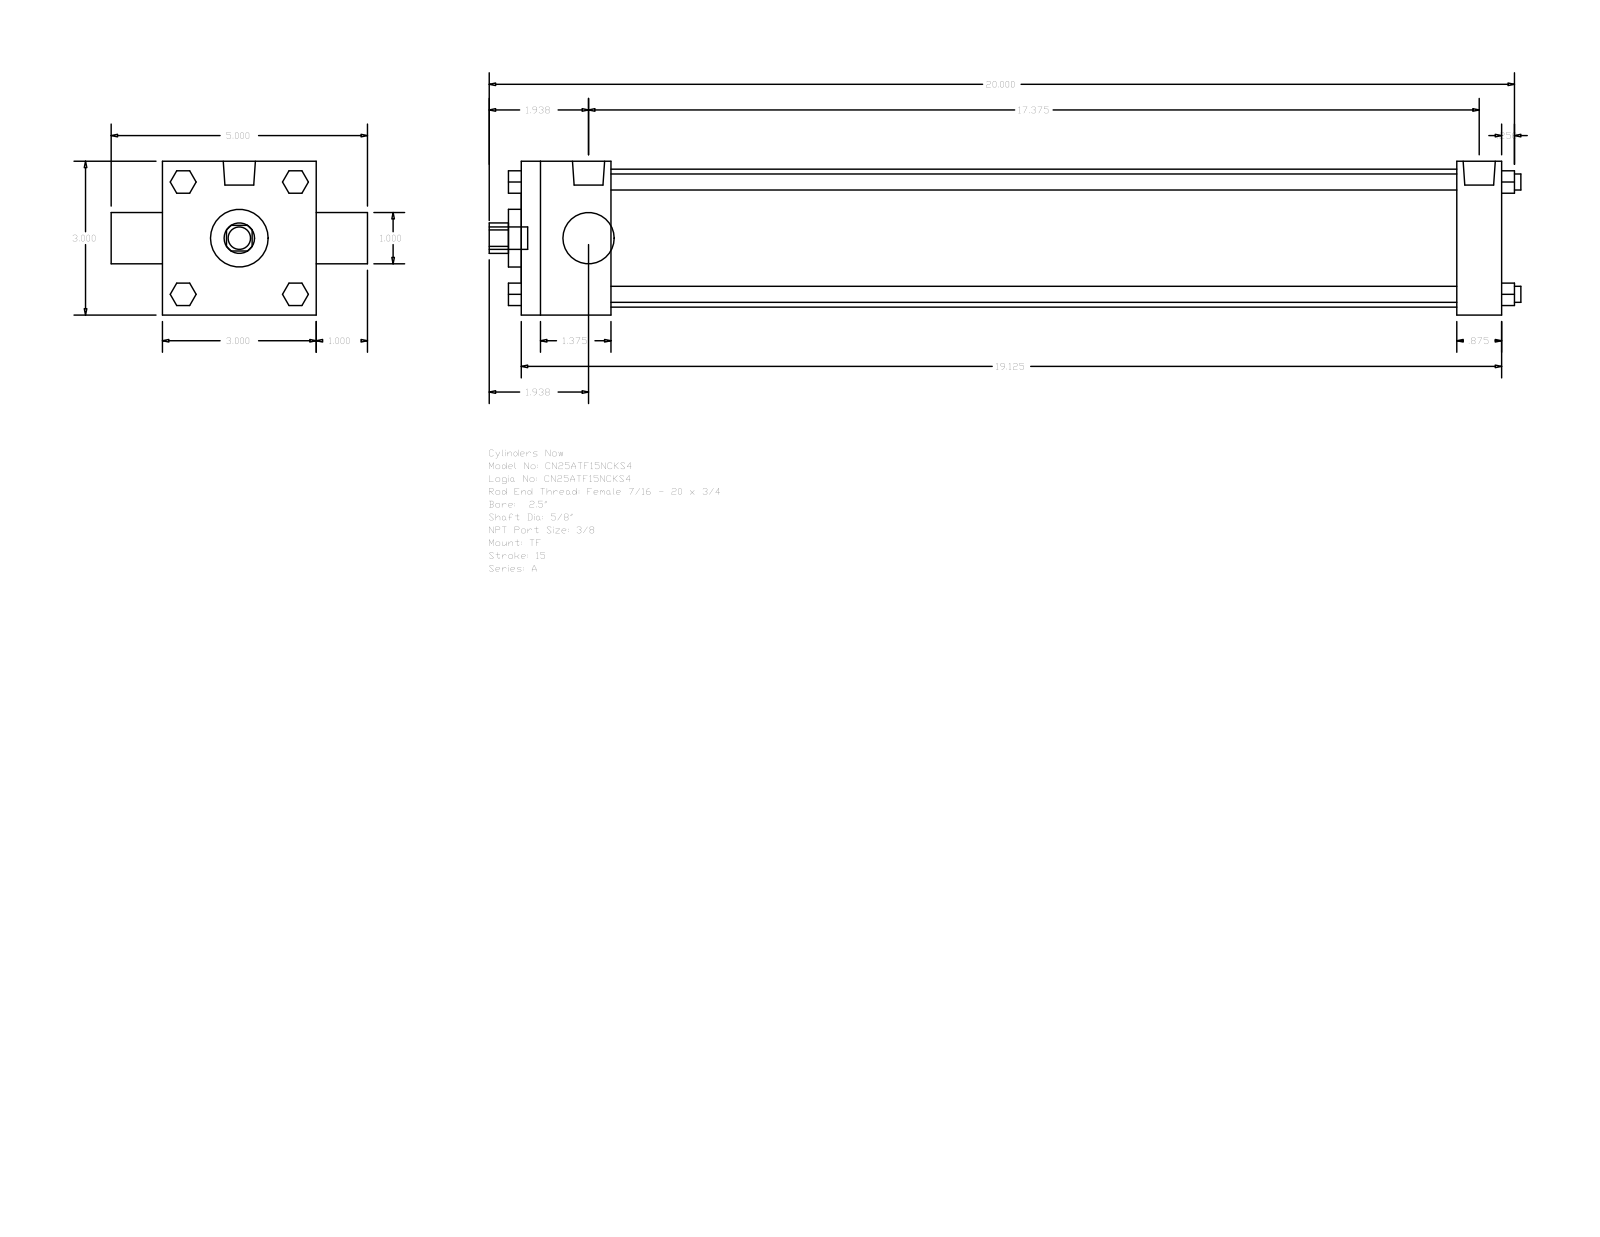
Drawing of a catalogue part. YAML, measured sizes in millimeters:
part_name: "A_TF__0250_0.625"
step_written_by: "GSSL Pune (CONFIG_CONTROL_DESIGN)"
units: millimeters
bodies: {solids: 0, faces: 120, planar: 92, cylindrical: 28, other: 0}
overall_size: [511.18, 127, 76.2]
round_holes:
  - {diameter: 15.88, count: 1}
  - {diameter: 25.4, count: 1}
  - {diameter: 28.57, count: 1}
  - {diameter: 68.33, count: 1}
round_bosses_or_shafts:
  - {diameter: 7.94, count: 4}
  - {diameter: 5.56, count: 3}
  - {diameter: 15.93, count: 2}
  - {diameter: 11.11, count: 1}
partial_cylinders:
  - {radius: 7.54, count: 1}
face_to_face_distances: [76.2, 485.77, 44.45, 463.55, 419.1, 441.32, 22.22, 25.4, 101.6, 6.35]
